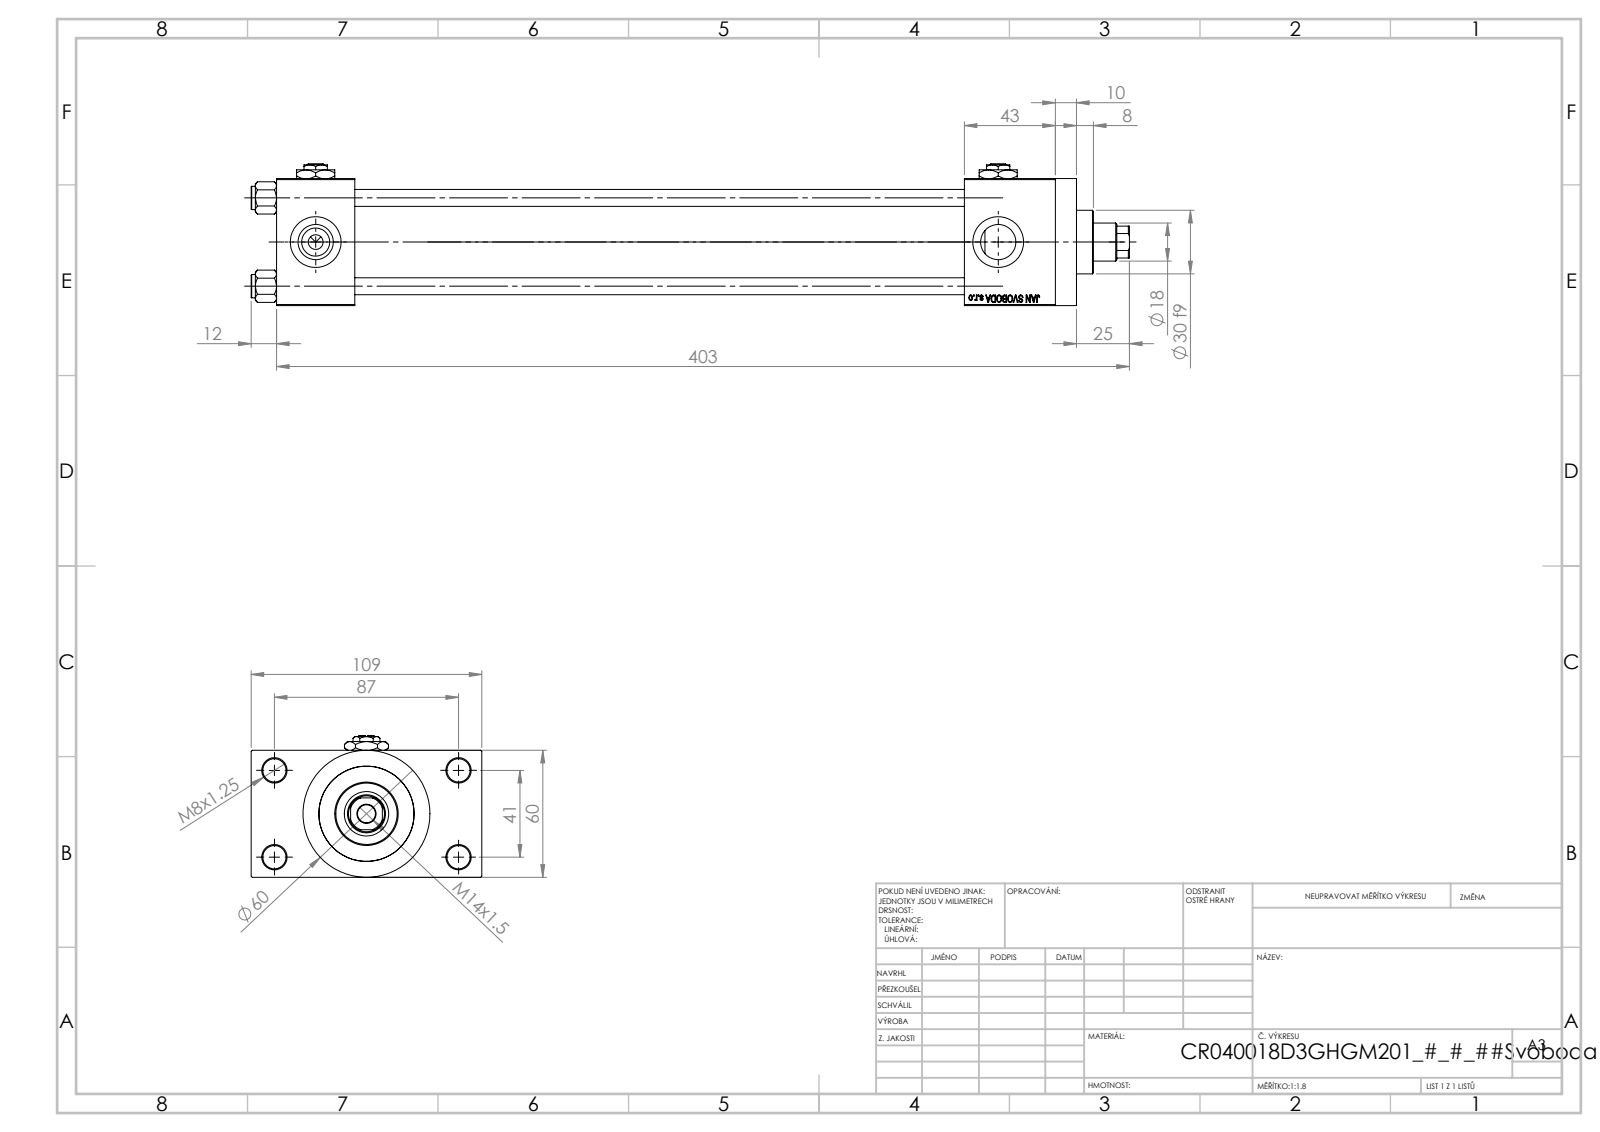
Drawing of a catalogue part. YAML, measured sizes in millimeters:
part_name: "NUT_M5_D; V215_VC_A; Zatka_pro_OIL_PORT; V215CR_D_TYCINKA (+2 more)"
step_written_by: "SolidWorks 2019 (CONFIG_CONTROL_DESIGN)"
units: millimeters
bodies: {solids: 13, faces: 1205, planar: 546, cylindrical: 99, other: 560}
overall_size: [415, 109, 67]
volume: 708320
surface_area: 223461
round_holes:
  - {diameter: 8, count: 4}
  - {diameter: 11, count: 4}
  - {diameter: 16.66, count: 4}
  - {diameter: 24, count: 4}
  - {diameter: 7, count: 3}
  - {diameter: 8.5, count: 1}
  - {diameter: 18, count: 1}
  - {diameter: 21, count: 1}
  - {diameter: 31, count: 1}
  - {diameter: 40, count: 1}
  - {diameter: 45, count: 1}
round_bosses_or_shafts:
  - {diameter: 11, count: 4}
  - {diameter: 60, count: 1}
  - {diameter: 46, count: 1}
  - {diameter: 30, count: 1}
partial_cylinders:
  - {radius: 8.5, count: 1}
face_to_face_distances: [60, 288, 24.5, 84.5, 37, 325, 43, 368, 331, 10]
hole_center_spacings: [22.65, 29.49, 41.7, 47.15, 48.09, 64.35, 76.49, 41]
